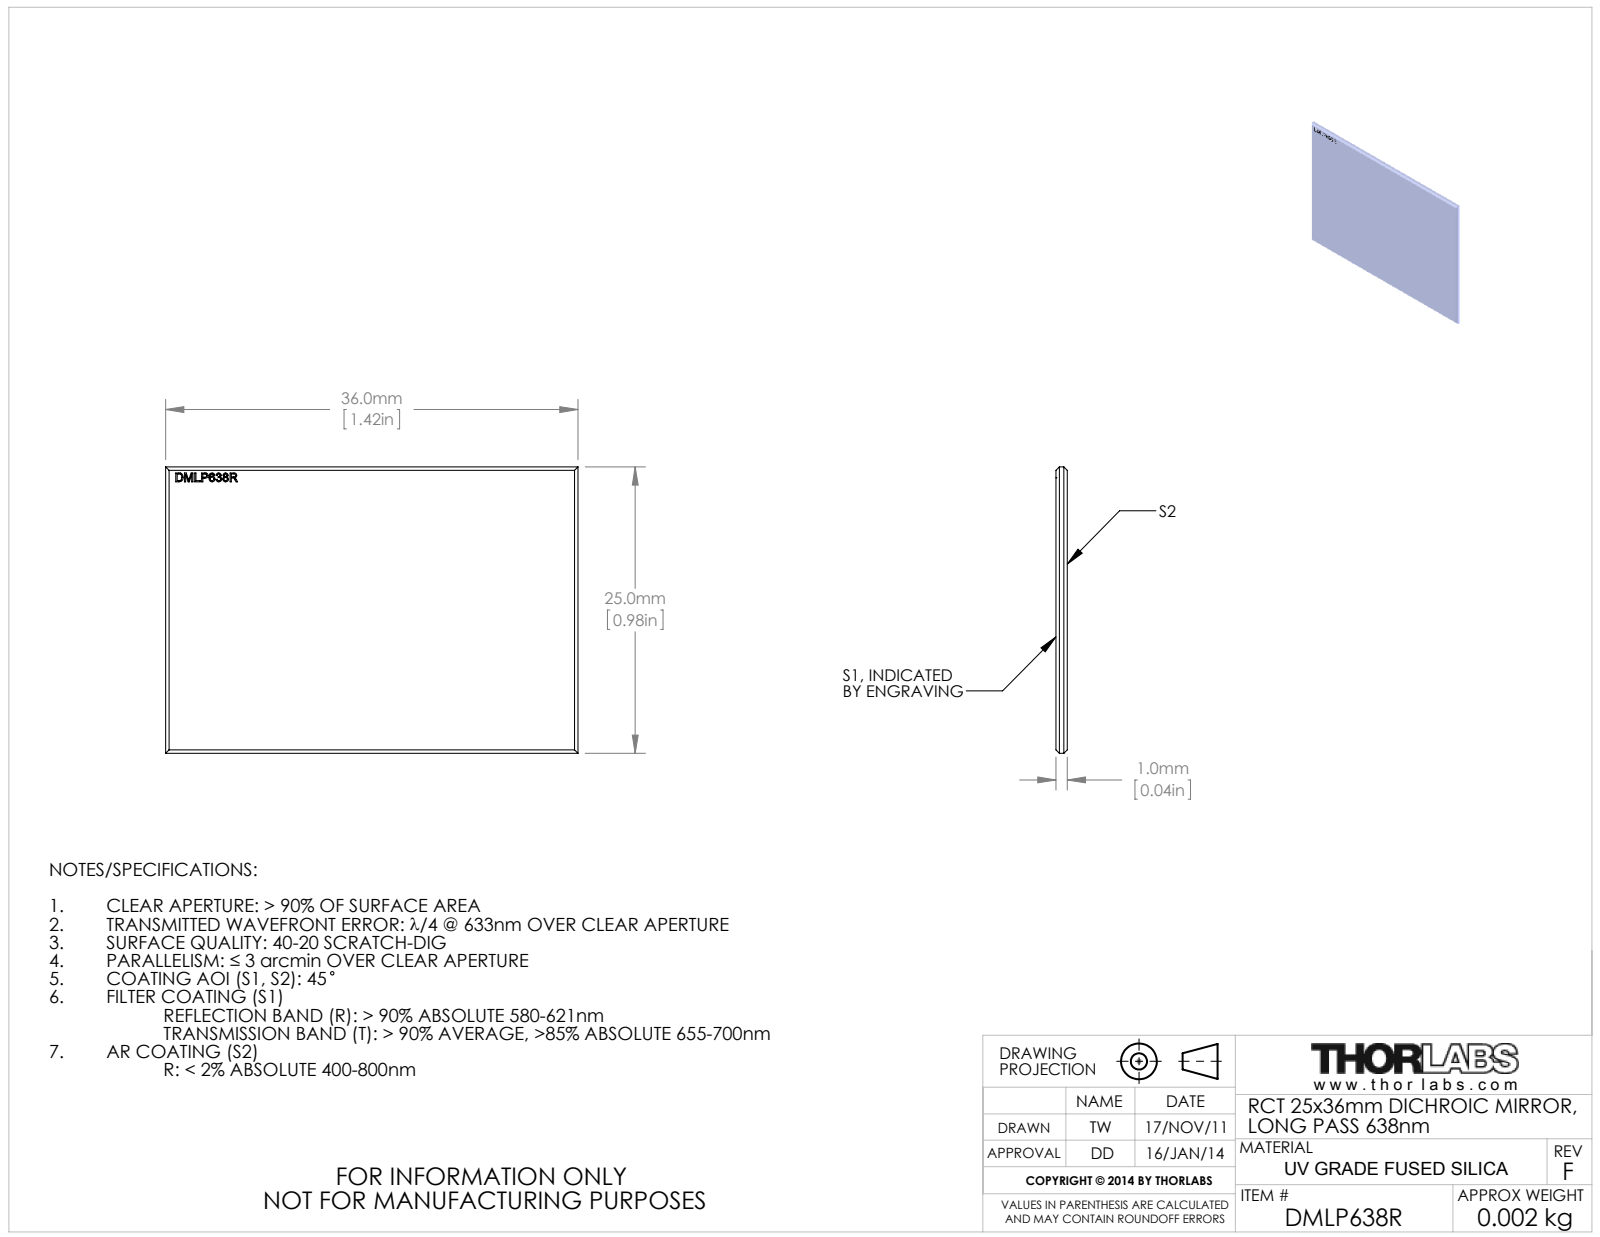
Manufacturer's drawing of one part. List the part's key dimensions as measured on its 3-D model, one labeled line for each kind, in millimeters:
Part name (STEP PRODUCT): 21099-E0W
STEP written by: SolidWorks 2011 (CONFIG_CONTROL_DESIGN)
Units: millimetres
Bodies: 0 solids, 53 faces (35 planar, 0 cylindrical, 18 other)
Overall size (bounding box): 36 × 25 × 1
Main face-to-face distances: 1, 18, 18, 25, 25.7, 25.7, 36, 1, 1.7, 34.4
